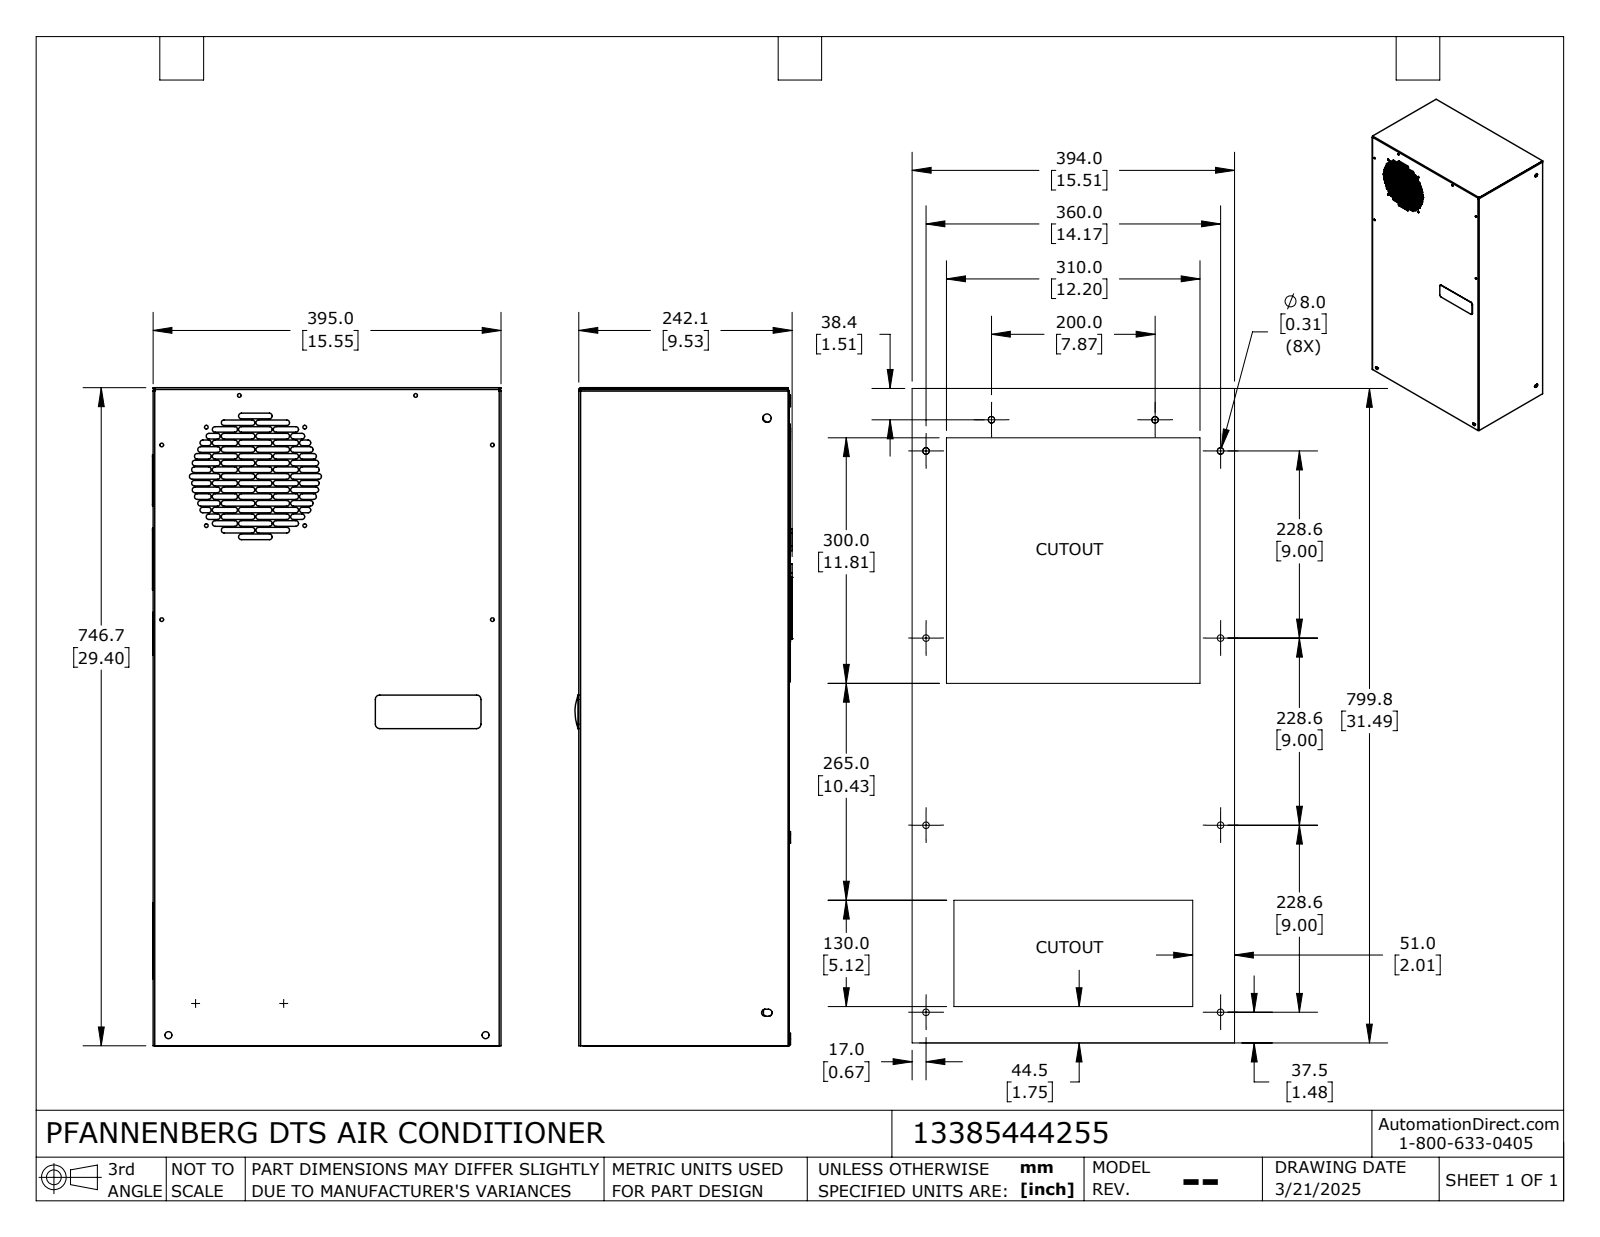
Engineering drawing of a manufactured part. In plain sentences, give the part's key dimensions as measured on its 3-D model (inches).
The part is named "13385444255_Default". Its 3-D file was written by "SolidWorks 2024 (CONFIG_CONTROL_DESIGN)". It is 1 solid with 1943 faces: 1110 planar, 805 cylindrical and 28 other. Overall it measures 29.397 by 15.571 by 9.704 inches. Its volume is 4 068 cubic inches and its surface area 5 117 square inches. Round holes: 20 of diameter 0.165, 12 of diameter 0.161, 10 of diameter 0.283, 6 of diameter 0.157, 4 of diameter 0.197, 2 of diameter 0.315, 2 of diameter 0.437, 1 of diameter 0.318, 1 of diameter 0.375, 1 of diameter 0.825, 1 of diameter 1, 1 of diameter 1.25. Round bosses or shafts: 10 of diameter 0.512. Partial cylindrical surfaces (rounded edges, fillets, slot ends): 140 of radius 0.125, 130 of radius 0.112, 18 of radius 0.031, 18 of radius 0.079, 16 of radius 0.085, 12 of radius 0.079, 12 of radius 0.197, 10 of radius 0.113. The main face-to-face distances are 0.048, 15.504, 0.036, 9.026, 9.243, 0.217, 9.29, 0.264, 0.115, 9.141. The hole center spacings are 4.398, 0.172, 0.243, 4.669, 6.22, 7.802, 7.874, 9.012.
